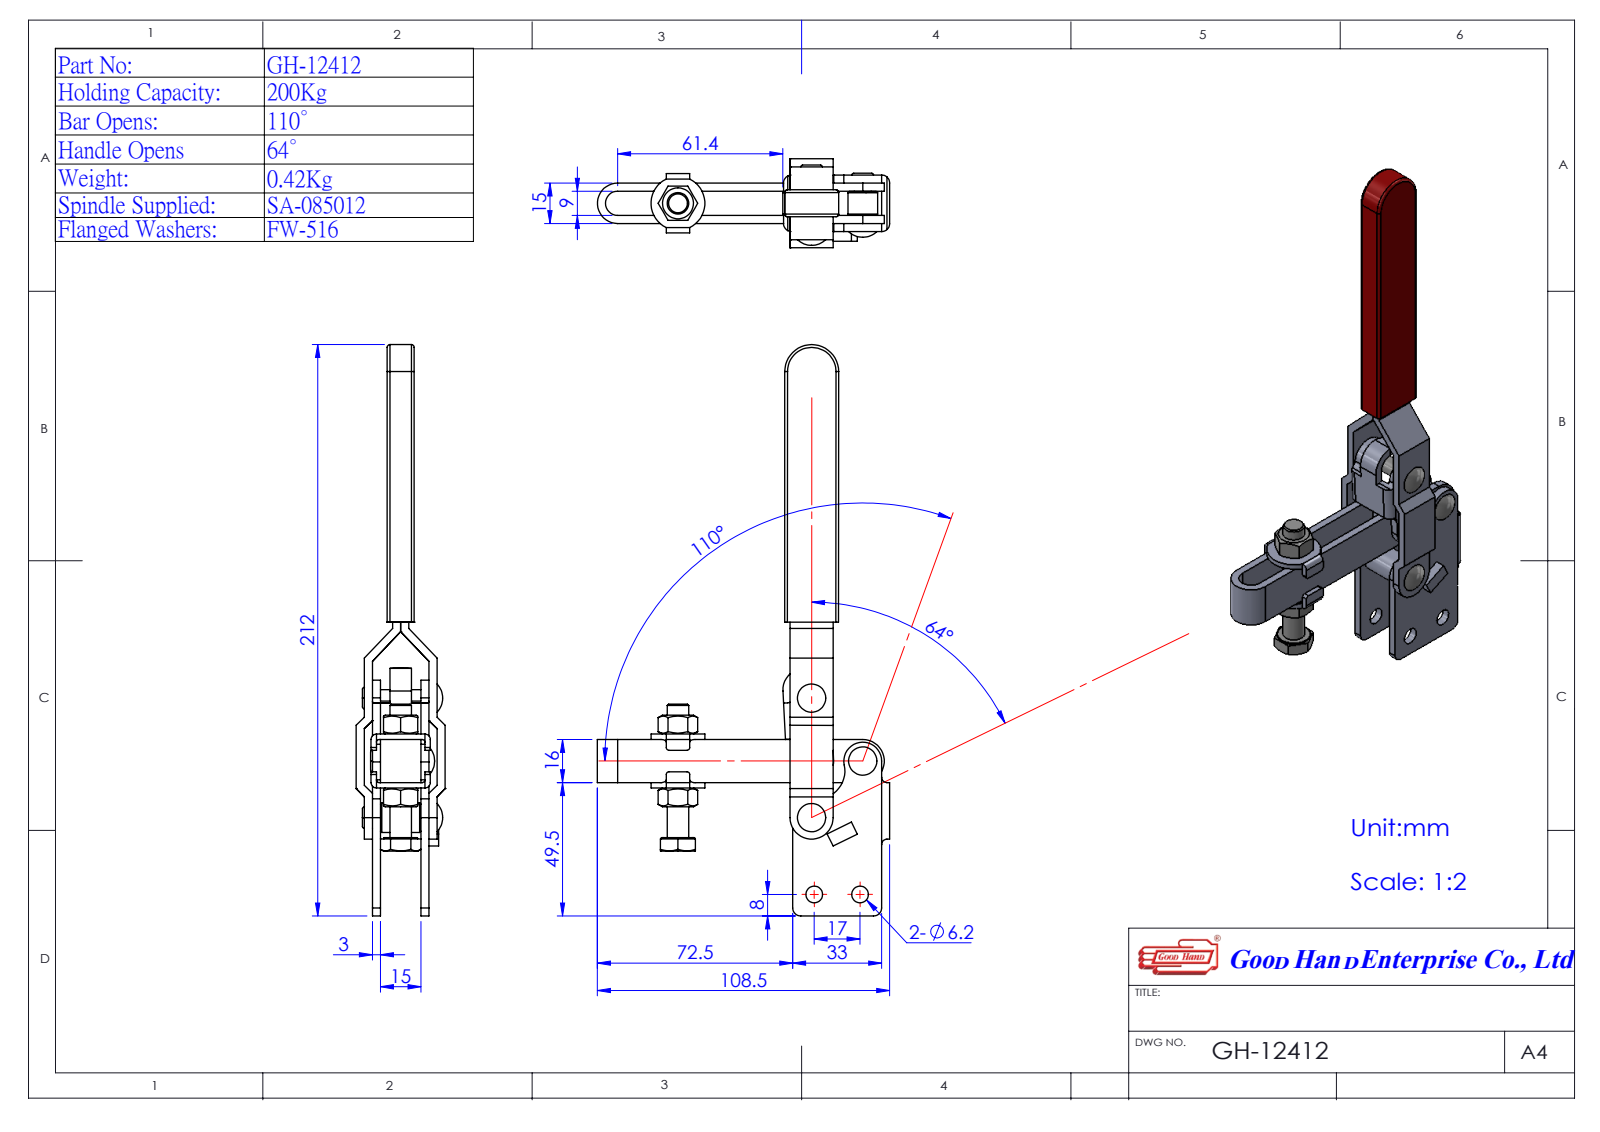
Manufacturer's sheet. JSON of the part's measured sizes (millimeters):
{"part_name": "Group2^GH-12412(簡化)-1; Group1^GH-12412(簡化)-1; Group4^GH-12412(簡化)-1; 11141208-1^GH-12412(簡化)-1 (+2 more)", "step_written_by": "SolidWorks 2016 (AUTOMOTIVE_DESIGN)", "units": "millimeters", "bodies": {"solids": 5, "faces": 251, "planar": 124, "cylindrical": 97, "other": 30}, "overall_size": [212, 108.5, 33], "volume_mm3": 60313, "surface_area_mm2": 37516, "round_holes": [[4, 4], [6.2, 2]], "round_bosses_or_shafts": [[12.5, 1], [8, 1]], "partial_cylinders_radius": [[1, 8], [2, 8], [3, 6], [7, 4], [8, 2], [10, 2], [4.5, 1], [7.5, 1]], "face_to_face_distances": [3, 18, 15, 6, 21, 5.5, 2.5, 15.5, 12.5, 9], "hole_center_spacings": [17, 17.8, 21.03, 23.38, 28.32, 28.52, 30.09, 33.71]}
